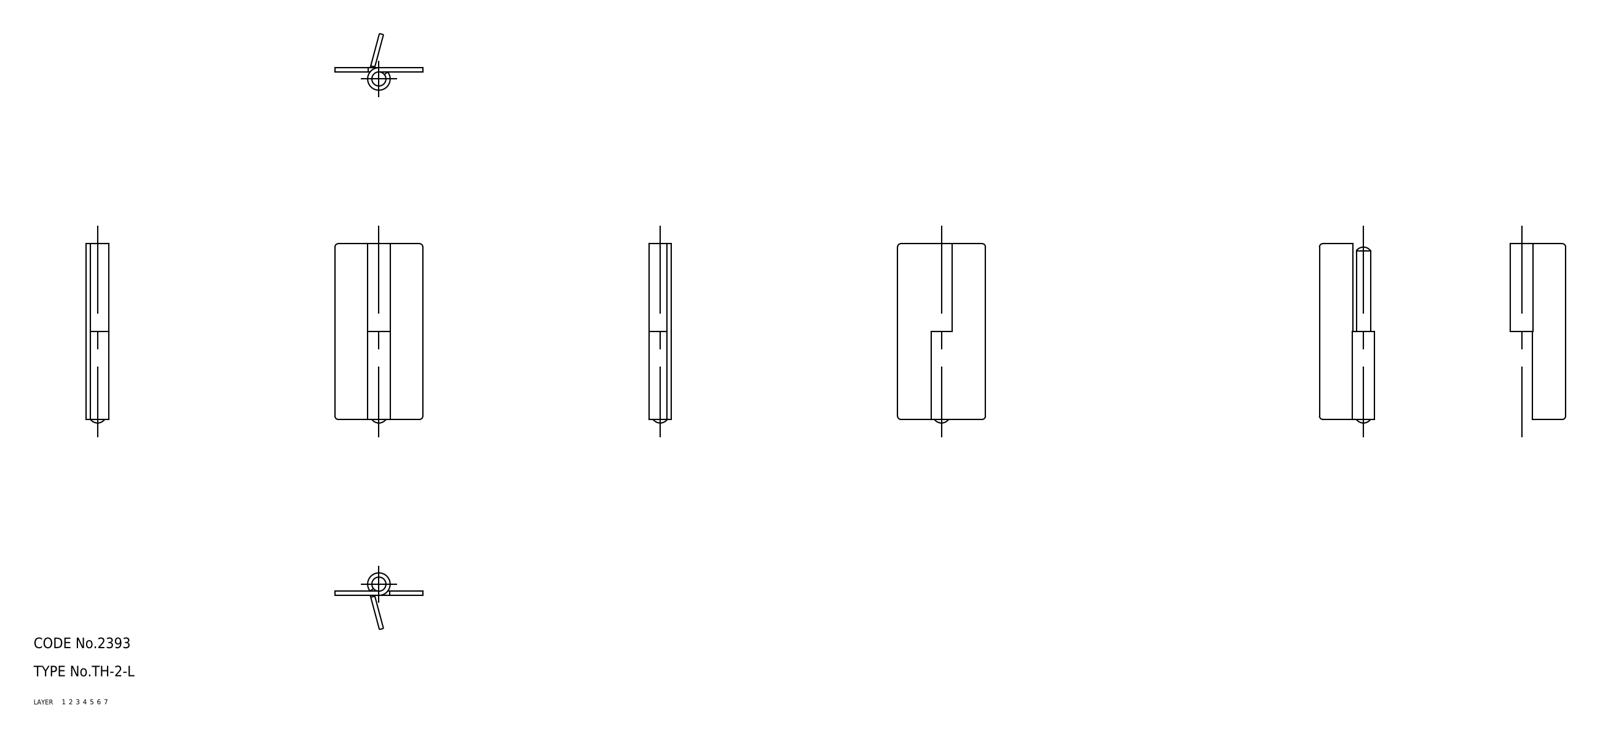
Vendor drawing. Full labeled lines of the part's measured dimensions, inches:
Part name (STEP PRODUCT): shaft; hinge piece_B; hinge piece_A; TH_2_L_7364_36
STEP written by: CADfix (AUTOMOTIVE_DESIGN)
Units: inches
Bodies: 3 solids, 28 faces (0 planar, 0 cylindrical, 28 other)
Overall size (bounding box): 2.008 × 0.984 × 0.252
Volume: 0.169 in³ · Surface area: 7.121 in²
